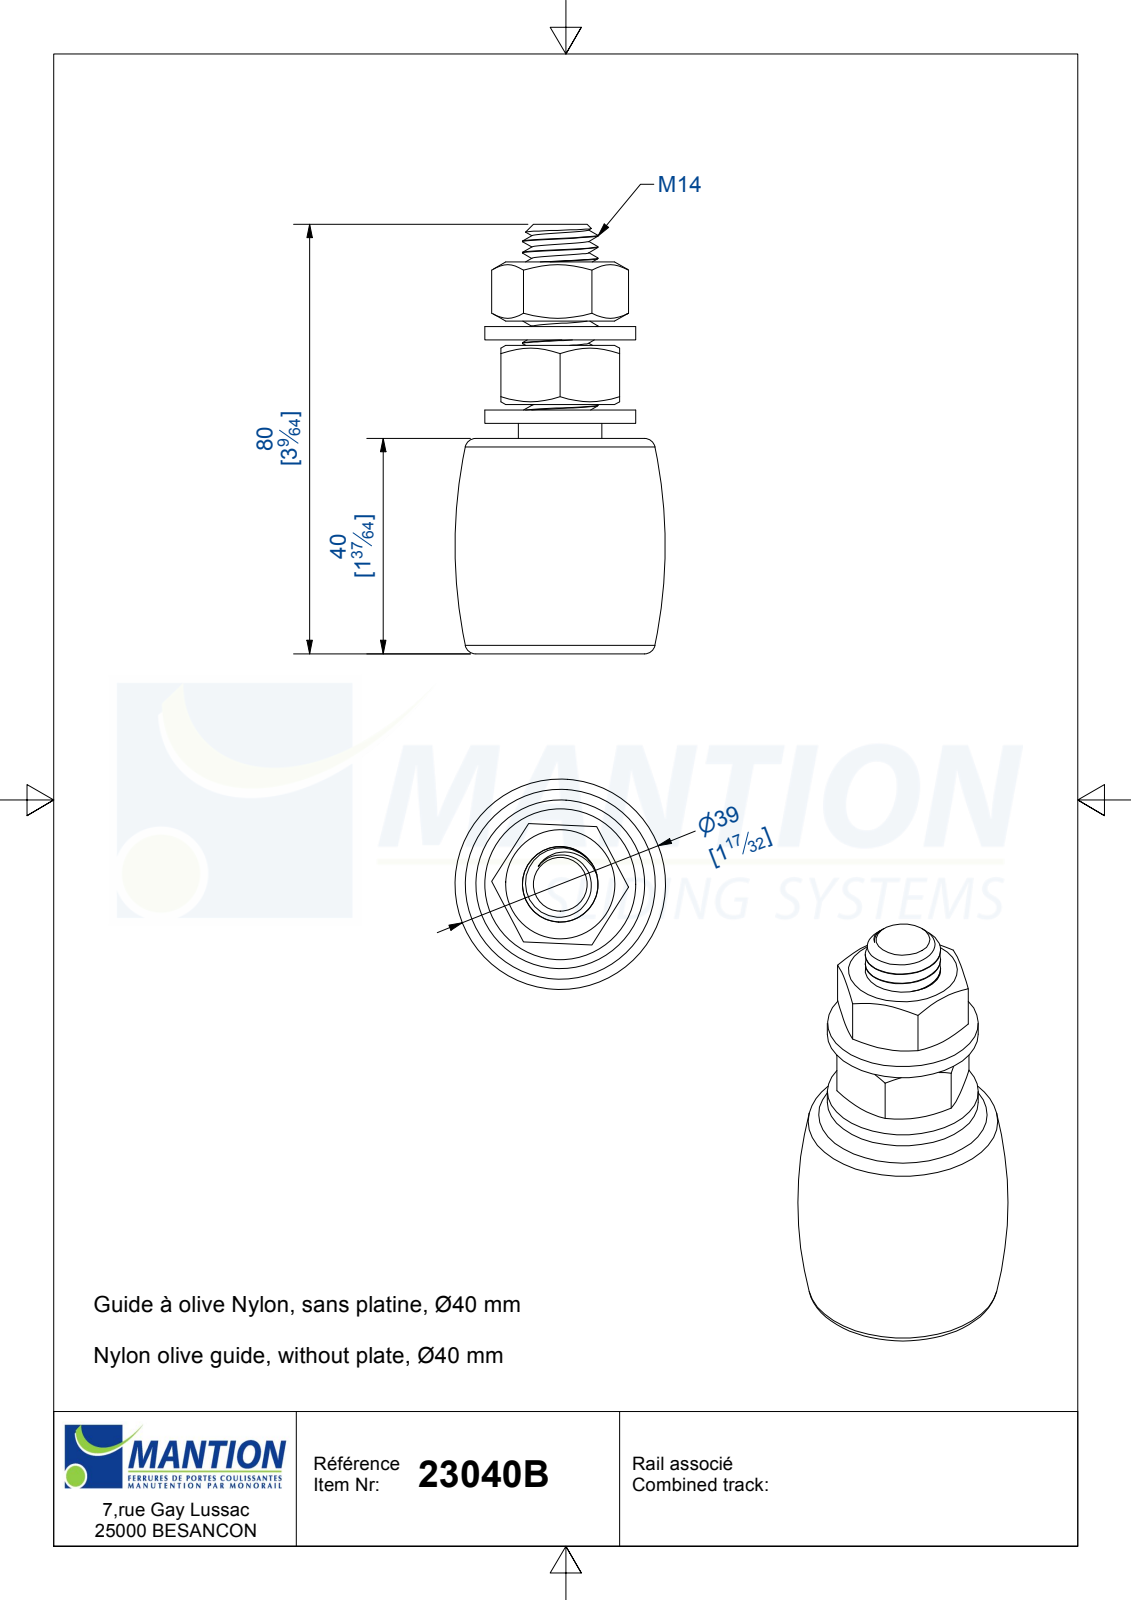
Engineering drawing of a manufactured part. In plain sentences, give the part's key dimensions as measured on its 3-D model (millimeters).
The part is named "23040B; 23040B-OLIVE; local.DIN.126.16.8; Rondelle_14_ISO7091 (+1 more)". Its 3-D file was written by "Autodesk Inventor 2019 (AUTOMOTIVE_DESIGN)". It is 6 solids with 65 faces: 35 planar, 12 cylindrical and 18 other. Overall it measures 79.76 by 39 by 39 millimeters. Its volume is 54 308 cubic millimeters and its surface area 19 852 square millimeters. Round holes: 1 of diameter 11.84, 1 of diameter 15.5, 1 of diameter 16.5, 1 of diameter 25. Round bosses or shafts: 1 of diameter 28, 1 of diameter 14. The main face-to-face distances are 16.5, 2.5, 22, 27.5, 21.26, 4.76, 19, 23.76, 14, 7.26.
